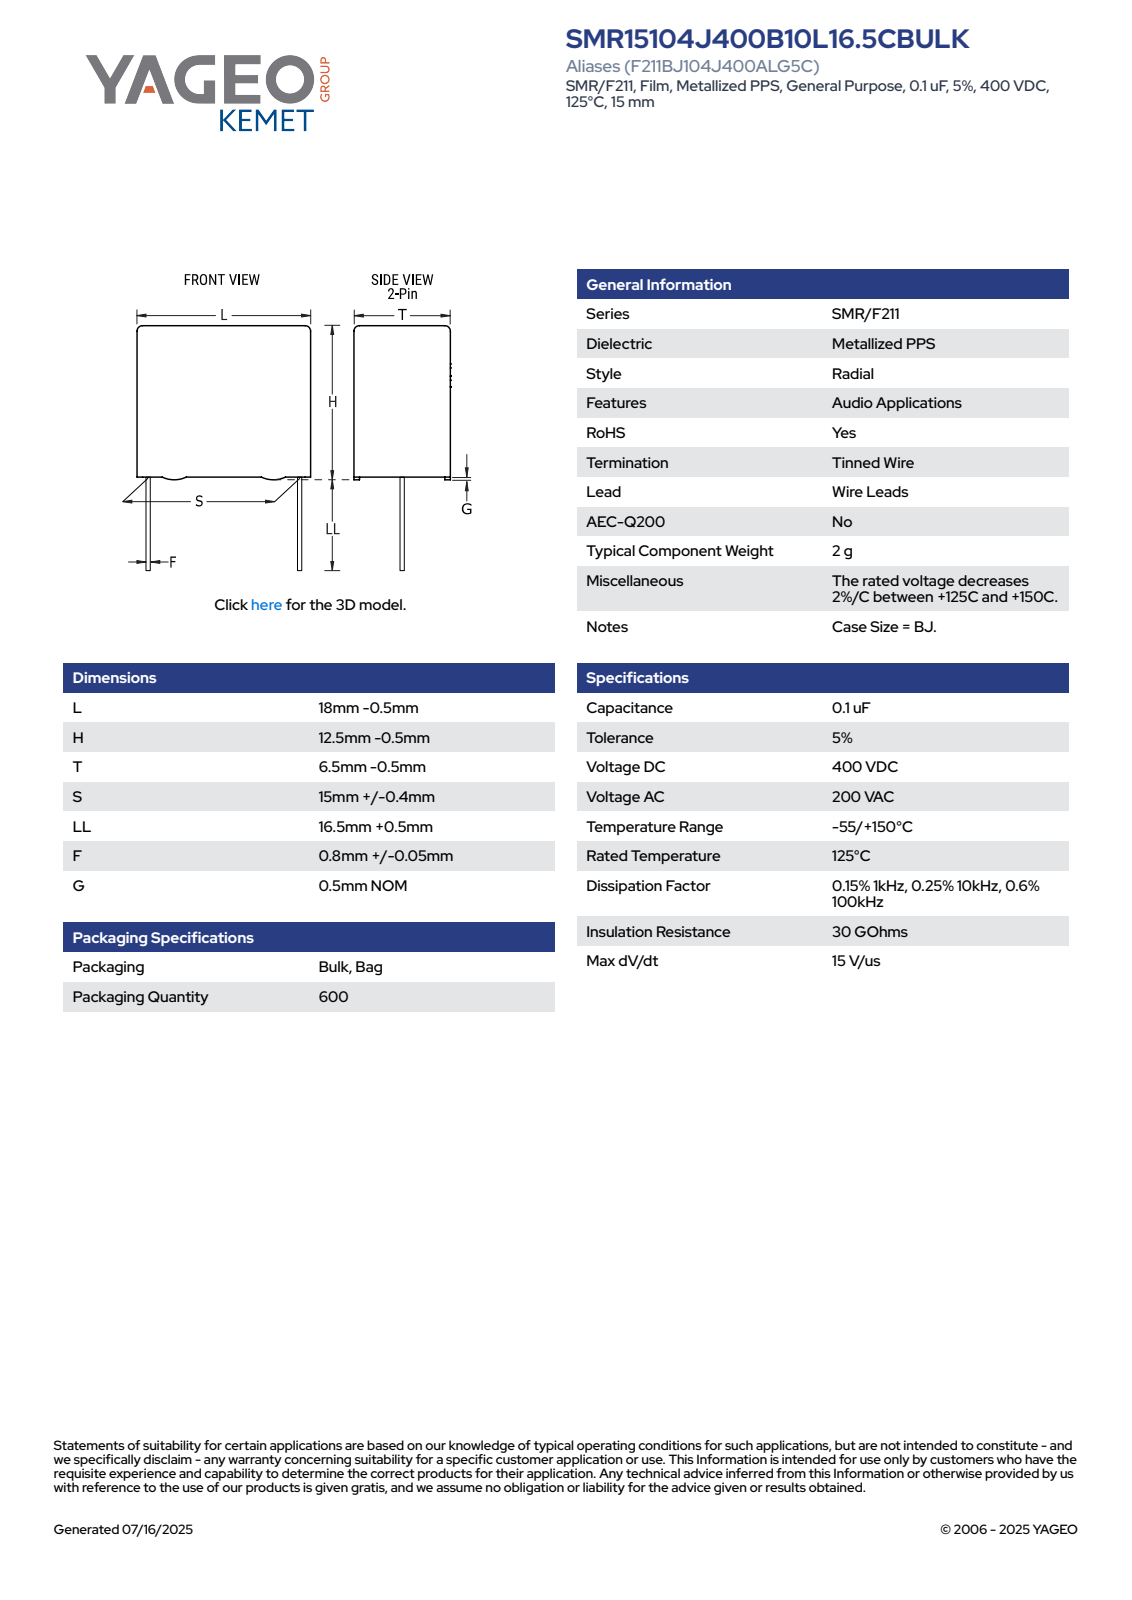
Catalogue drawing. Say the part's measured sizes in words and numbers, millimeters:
The part is named "CFR_RBG_18X12.5X6.5_L17.5H12T6S15LL17F0.85G0.5". Its 3-D file was written by "SolidWorks 2021 (AUTOMOTIVE_DESIGN)". It is 4 solids with 89 faces: 81 planar, 8 cylindrical and 0 other. Overall it measures 29 by 17.5 by 6 millimeters. Its volume is 1 227 cubic millimeters and its surface area 879 square millimeters. Round bosses or shafts: 2 of diameter 0.85. Partial cylindrical surfaces (rounded edges, fillets, slot ends): 4 of radius 0.5. The main face-to-face distances are 6, 11.5, 17.5, 0.34, 5.66, 0.5, 12, 5.32, 17, 29.
